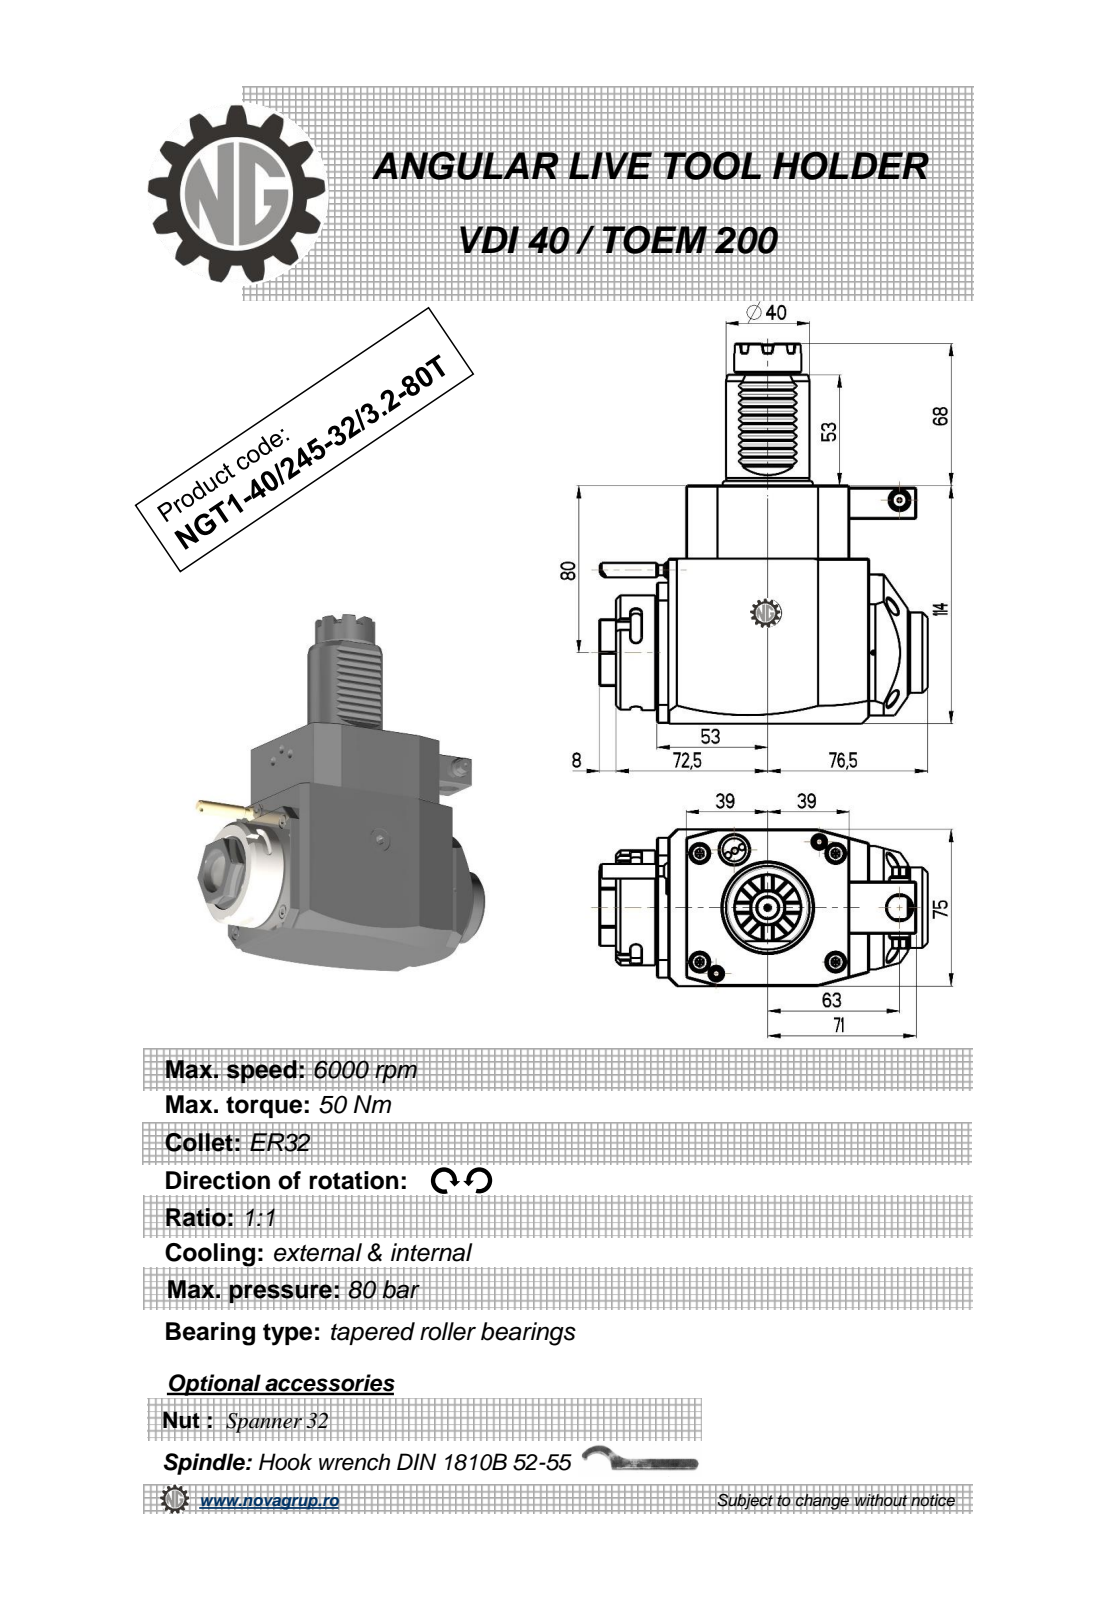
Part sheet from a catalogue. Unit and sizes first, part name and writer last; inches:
Units: inches
Overall size (bounding box): 7.165 × 6.181 × 2.953
Round holes (diameter × count): ⌀0.079 ×1, ⌀0.098 ×1, ⌀0.118 ×1, ⌀0.374 ×1, ⌀0.472 ×1, ⌀0.906 ×1
Round bosses / shafts (diameter × count): ⌀0.315 ×2, ⌀2.165 ×1, ⌀1.89 ×1, ⌀1.575 ×1, ⌀1.516 ×1, ⌀1.26 ×1, ⌀0.677 ×1, ⌀0.394 ×1
Partial cylindrical surfaces — rounded edges, fillets, slot ends (radius × count): R0.012 ×10, R0.098 ×6, R7.087 ×2, R0.02 ×1, R0.152 ×1, R0.167 ×1, R0.965 ×1, R1.476 ×1
Main face-to-face distances: 2.953, 4.488, 0.551, 3.622, 3.071, 0.984, 0.768, 1.319, 4.39, 1.378
Hole centre spacings: 1.47, 1.701, 2.854
Volume: 59.35 in³ · Surface area: 114.3 in²
Bodies: 1 solid, 423 faces (227 planar, 82 cylindrical, 114 other)
Part name (STEP PRODUCT): NGT1_40_245_32_3_2_80T
STEP written by: PRO/ENGINEER BY PARAMETRIC TECHNOLOGY CORPORATION, 2010280 (CONFIG_CONTROL_DESIGN)
